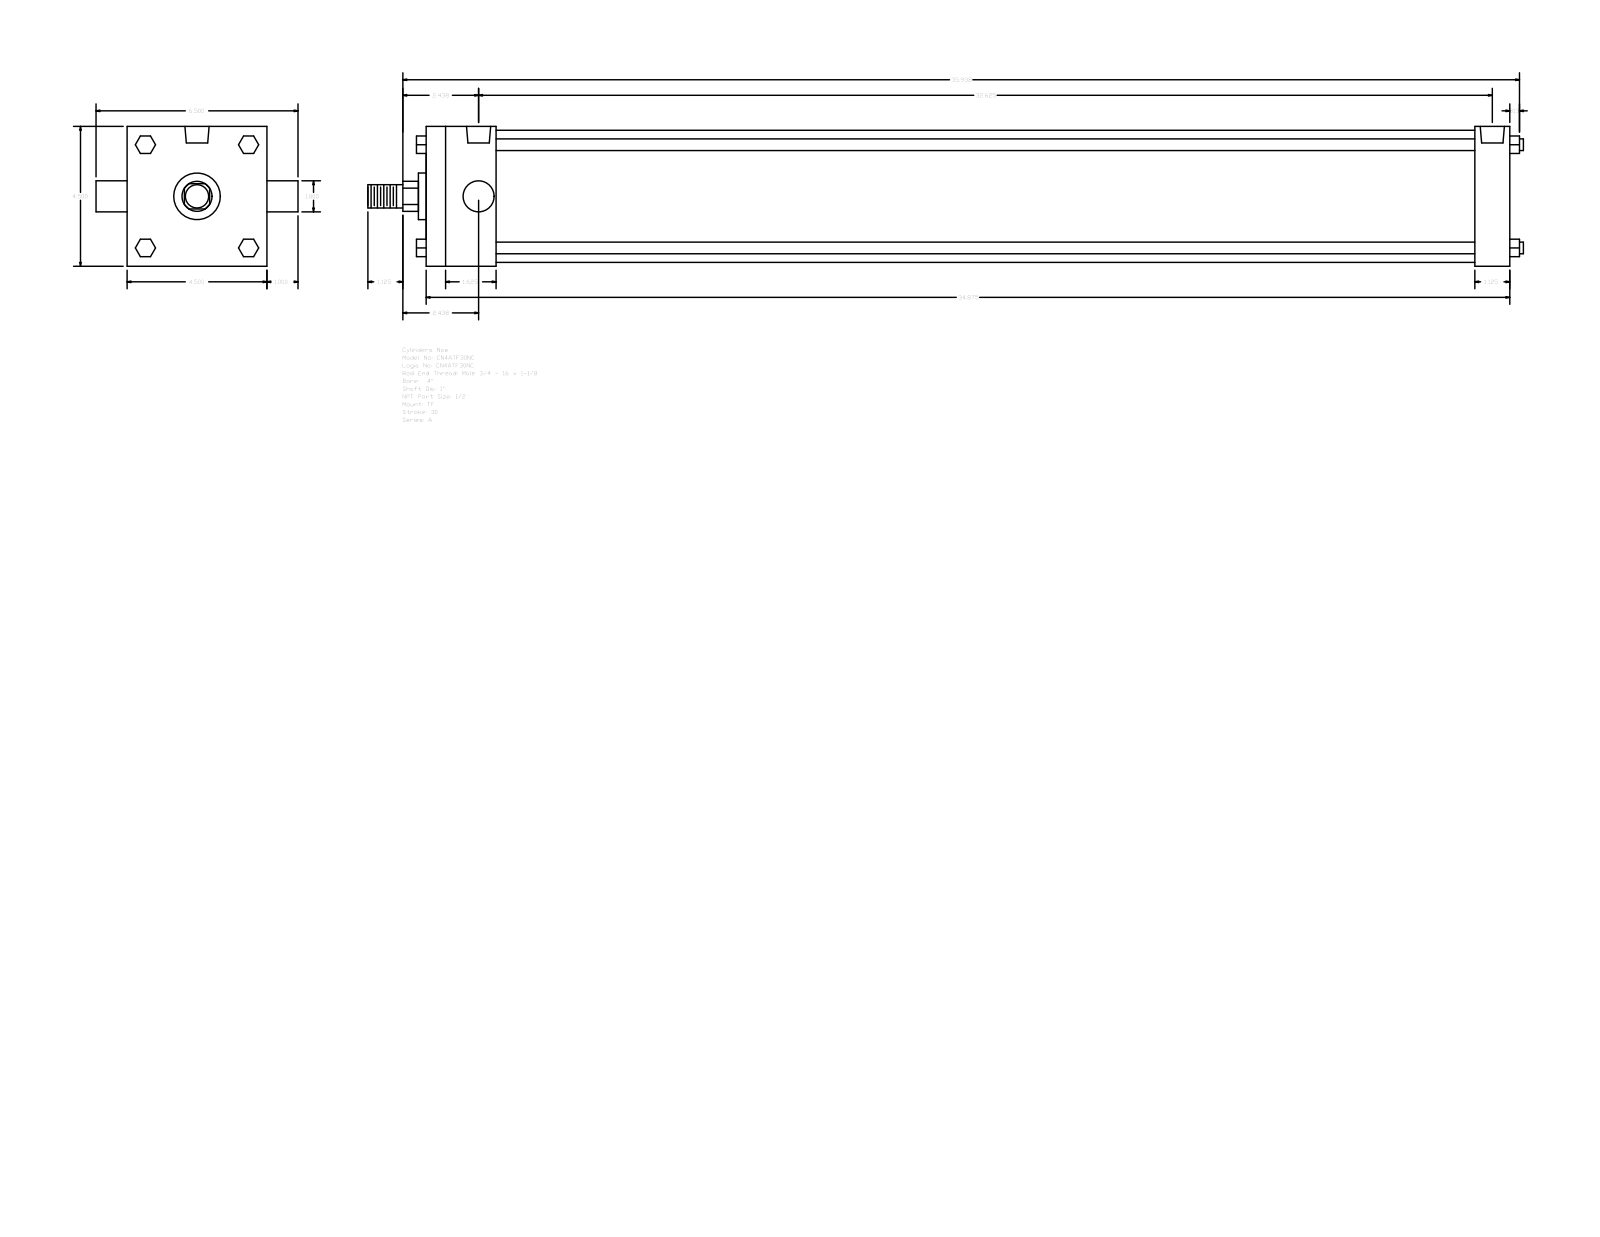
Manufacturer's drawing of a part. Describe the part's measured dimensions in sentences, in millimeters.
The part is named "A_TF__0400_1". Its 3-D file was written by "GSSL Pune (CONFIG_CONTROL_DESIGN)". It is 0 solids with 120 faces: 92 planar, 28 cylindrical and 0 other. Overall it measures 944.56 by 165.1 by 114.3 millimeters. Round holes: 3 of diameter 8.73, 2 of diameter 19.77. Round bosses or shafts: 4 of diameter 9.53, 2 of diameter 25.4, 1 of diameter 107.95, 1 of diameter 38.1, 1 of diameter 19.05. Partial cylindrical surfaces (rounded edges, fillets, slot ends): 1 of radius 12.29. The main face-to-face distances are 114.3, 885.83, 857.25, 28.58, 57.15, 800.1, 828.68, 14.29, 42.16, 73.03. The hole center spacings are 3.18, 825.5, 822.32, 828.68.
